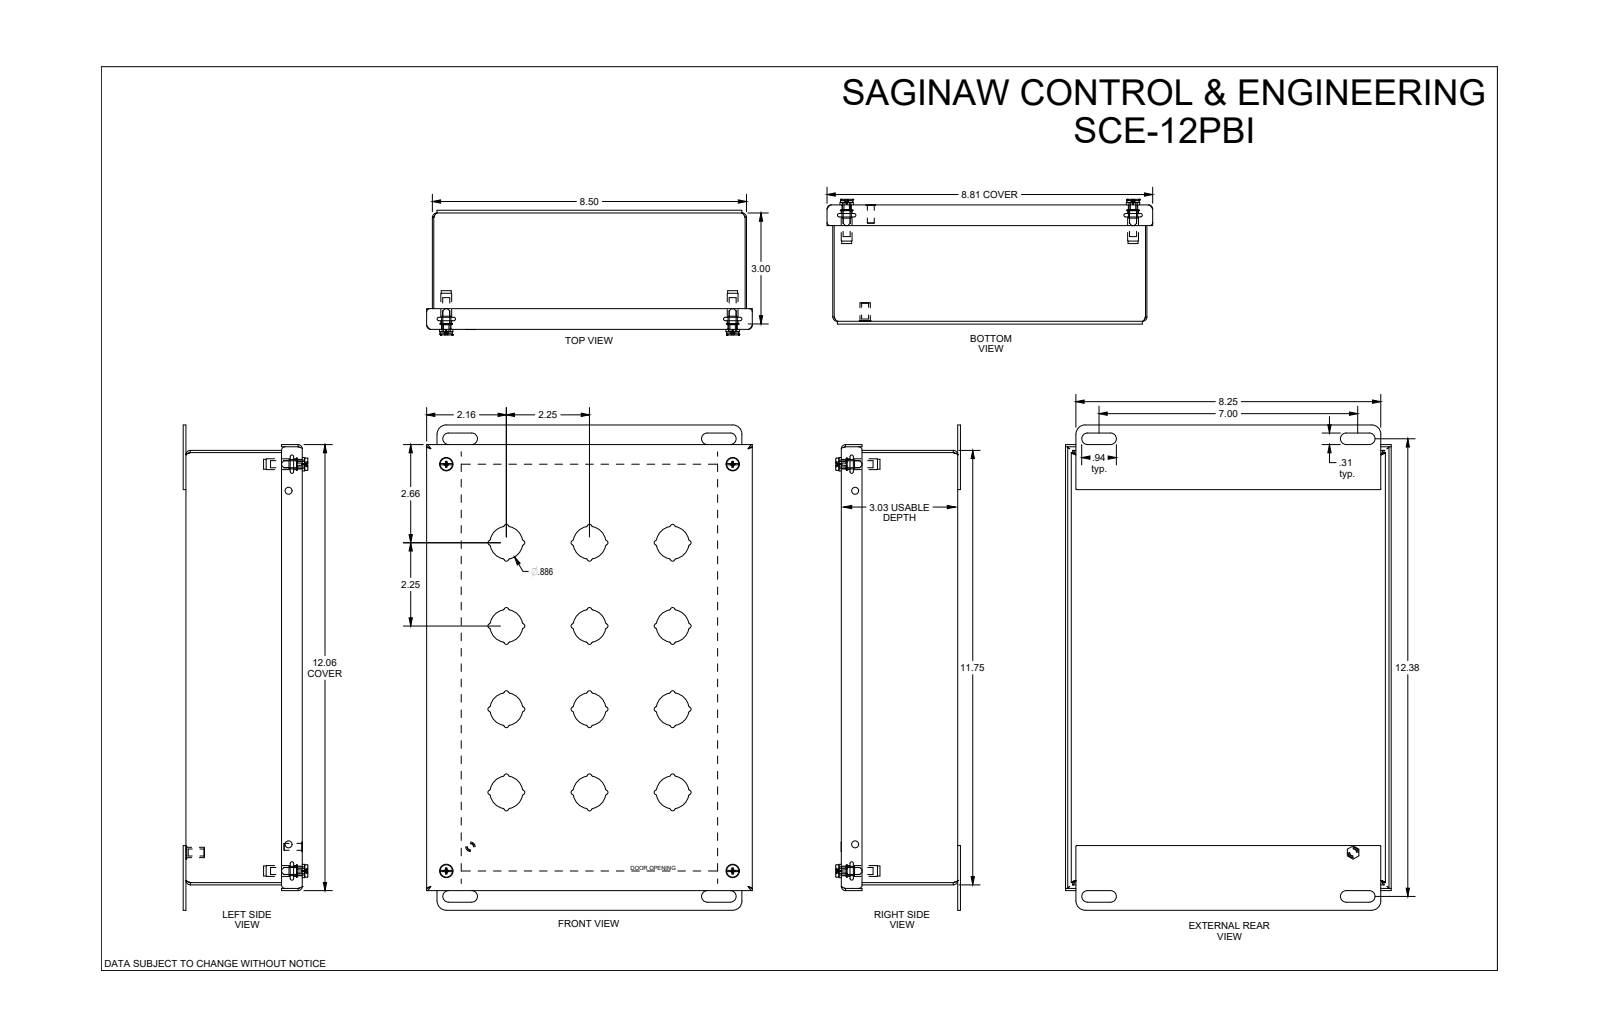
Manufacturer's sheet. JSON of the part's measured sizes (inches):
{"part_name": "SCE-12PBI", "step_written_by": "SolidWorks 2019 (AUTOMOTIVE_DESIGN)", "units": "inches", "bodies": {"solids": 15, "faces": 612, "planar": 166, "cylindrical": 370, "other": 76}, "overall_size": [13.125, 8.813, 3.286], "volume_in3": 24.58, "surface_area_in2": 813.3, "round_holes": [[0.19, 5], [0.22, 4], [0.25, 4], [0.266, 4], [0.317, 4], [0.193, 1], [0.28, 1]], "round_bosses_or_shafts": [[0.437, 4], [0.362, 4], [0.34, 4], [0.292, 4], [0.27, 4], [0.26, 4], [0.28, 1], [0.256, 1]], "partial_cylinders_radius": [[0.04, 96], [0.062, 48], [0.06, 20], [0.443, 12], [0.015, 8], [0.115, 8], [0.156, 8], [0.245, 8]], "face_to_face_distances": [0.06, 3.088, 3.028, 3.148, 8.44, 11.69, 2.94, 0.148, 0.156, 8.5], "hole_center_spacings": [7.75, 11, 11, 13.46, 7.757, 7.757, 13.456, 0.619]}
